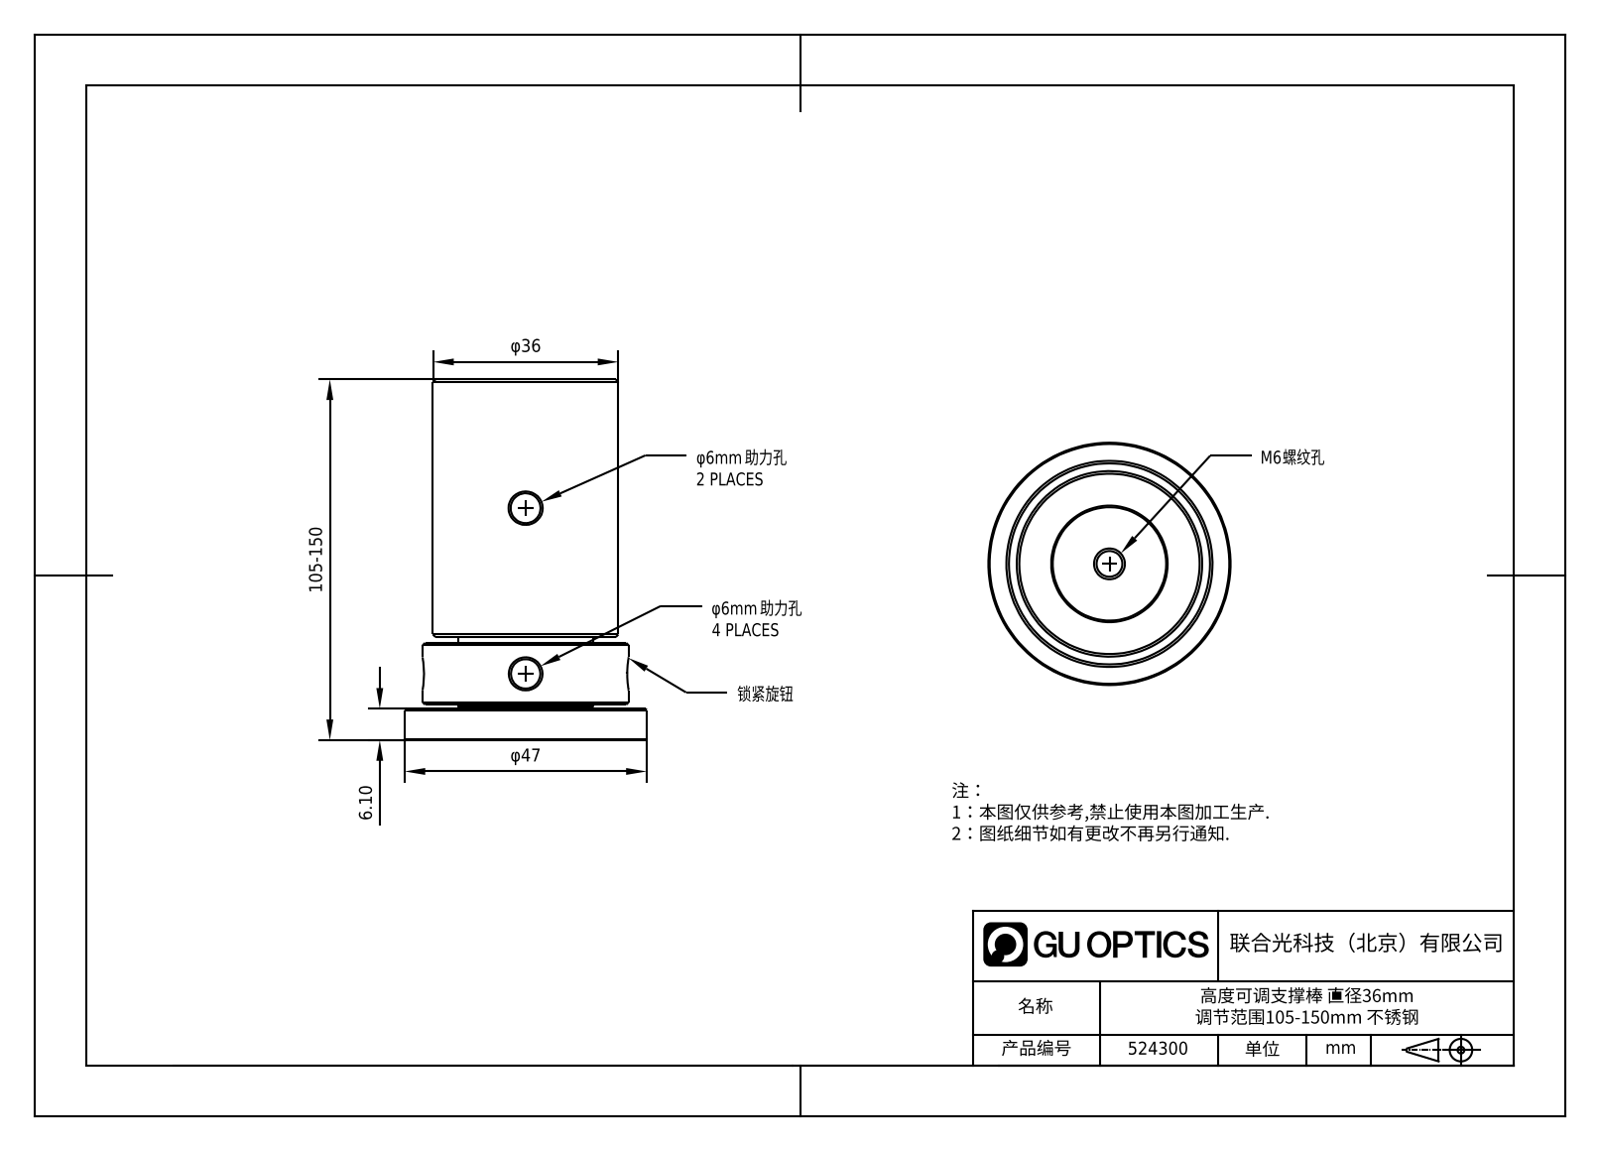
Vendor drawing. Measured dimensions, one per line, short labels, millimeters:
name: 7.6.4.1.3，1.5英寸高度可调支杆滚花旋钮，带SM1内螺纹，Rev.A; 7.6.4.1_ZGA-K1.5-108; 1.5英寸高度可调支杆立柱，带SM1外螺纹，Rev.A_7.6.4.1.2_1.5英寸高度可调支杆立柱，带SM1外螺纹; 1.4.6.3_ZGD-1.5B，1.5英寸支杆底座，带M6x6mm螺丝，A (+1 more)
written by: SolidWorks 2021 (CONFIG_CONTROL_DESIGN)
unit: mm
bodies: 4 solids, 117 faces (23 planar, 36 cylindrical, 58 other)
size: 95.04 × 47 × 47
volume: 104 118 mm³; area: 32 195 mm²
holes: 3× ⌀5.7, 1× ⌀5, 1× ⌀5.8, 1× ⌀25.4, 1× ⌀26.4
bosses: 1× ⌀47, 1× ⌀40, 1× ⌀36, 1× ⌀26.29, 1× ⌀6
face distances: 6.1, 81.54, 75.44, 18.1, 12, 63.44, 0.5, 95.04, 88.94, 76.94
